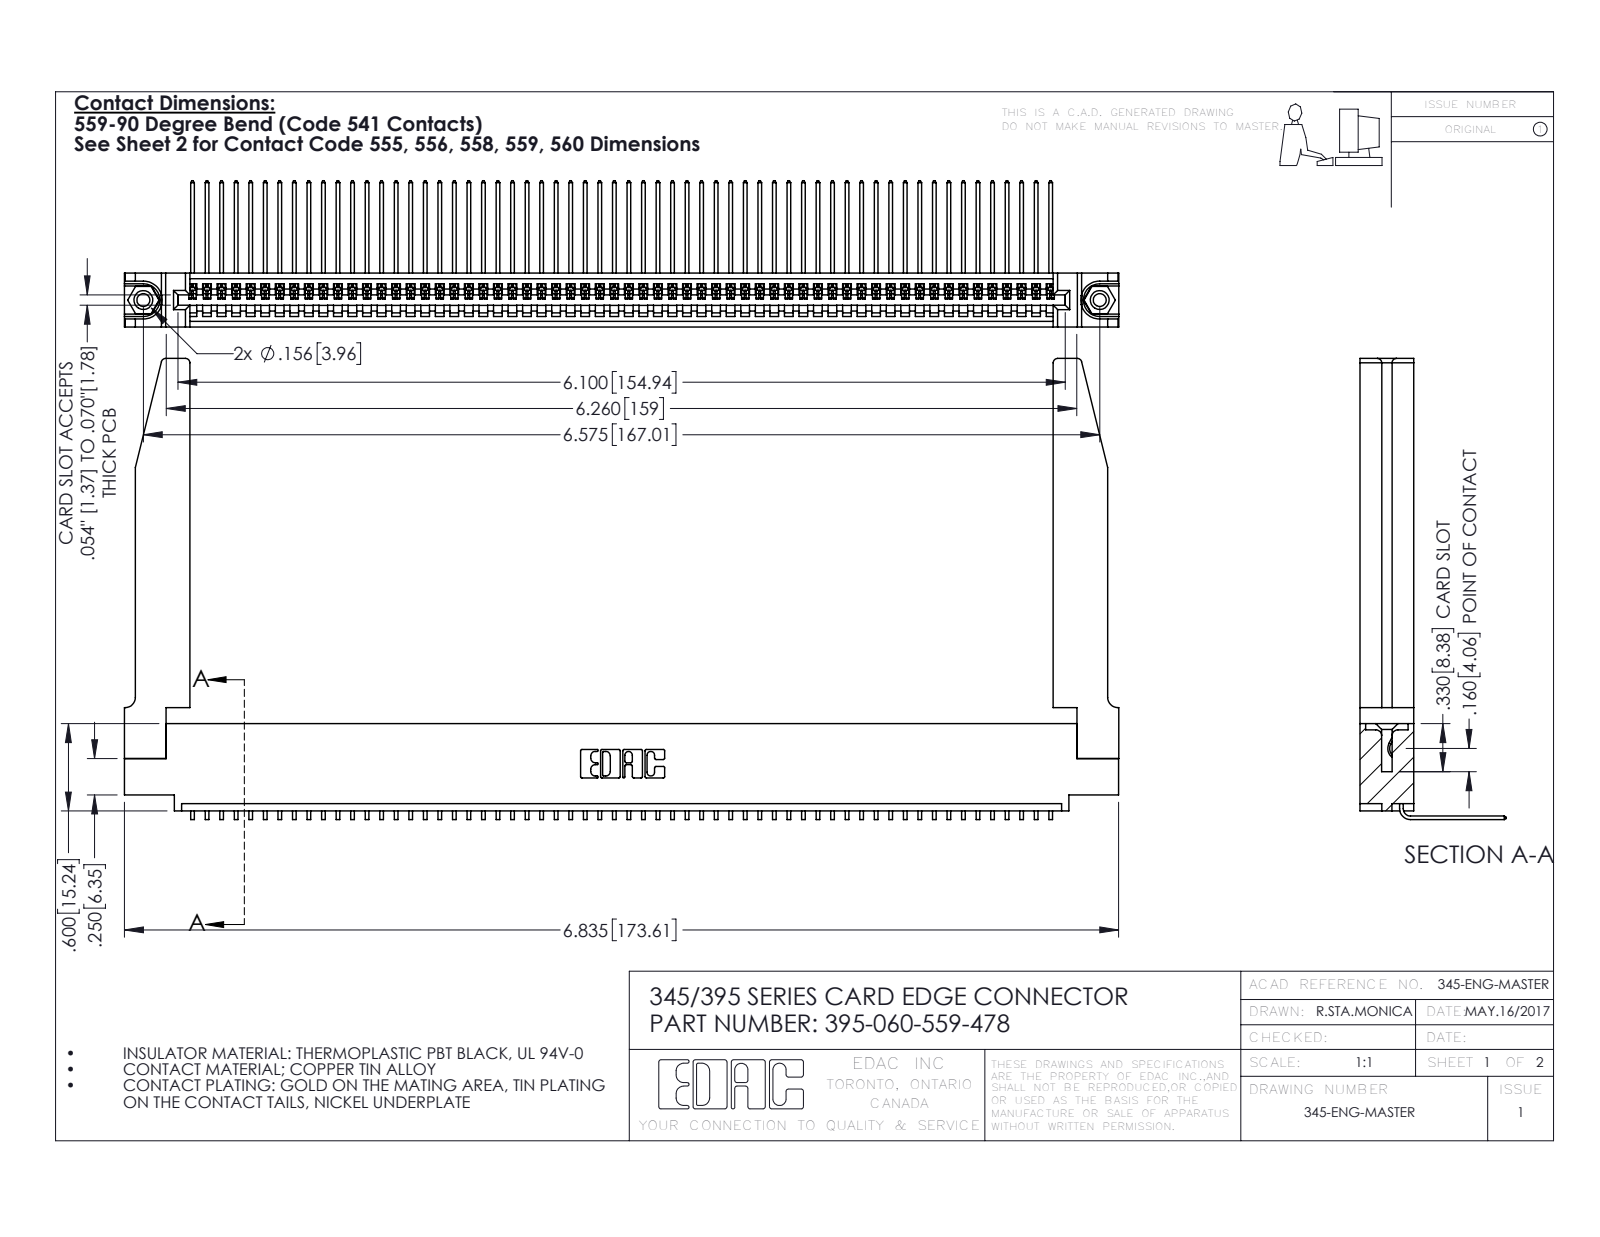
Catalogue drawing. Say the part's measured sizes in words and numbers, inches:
The part is named "345-250-001_345-250-001-102; 345-292-001_558 559 Tail - 1; 345 Part_0.110 Offset - 0.156 Dia-TH; 345-220-078_345-220-078 (+1 more)". Its 3-D file was written by "SolidWorks 2016 (CONFIG_CONTROL_DESIGN)". It is 65 solids with 3964 faces: 2746 planar, 1166 cylindrical and 52 other. Overall it measures 6.836 by 3.169 by 1.005 inches. Its volume is 1.497 cubic inches and its surface area 47.47 square inches. Round holes: 2 of diameter 0.089, 2 of diameter 0.125, 2 of diameter 0.156, 1 of diameter 0.064. Round bosses or shafts: 2 of diameter 0.155. Partial cylindrical surfaces (rounded edges, fillets, slot ends): 120 of radius 0.006, 22 of radius 0.01, 8 of radius 0.03, 6 of radius 0.007, 6 of radius 0.031, 3 of radius 0.026, 2 of radius 0.031, 2 of radius 0.04. The main face-to-face distances are 0.37, 0.072, 0.298, 0.098, 0.272, 0.025, 0.2, 0.225, 0.148, 0.15. The hole center spacings are 0.27, 6.339, 6.575.
